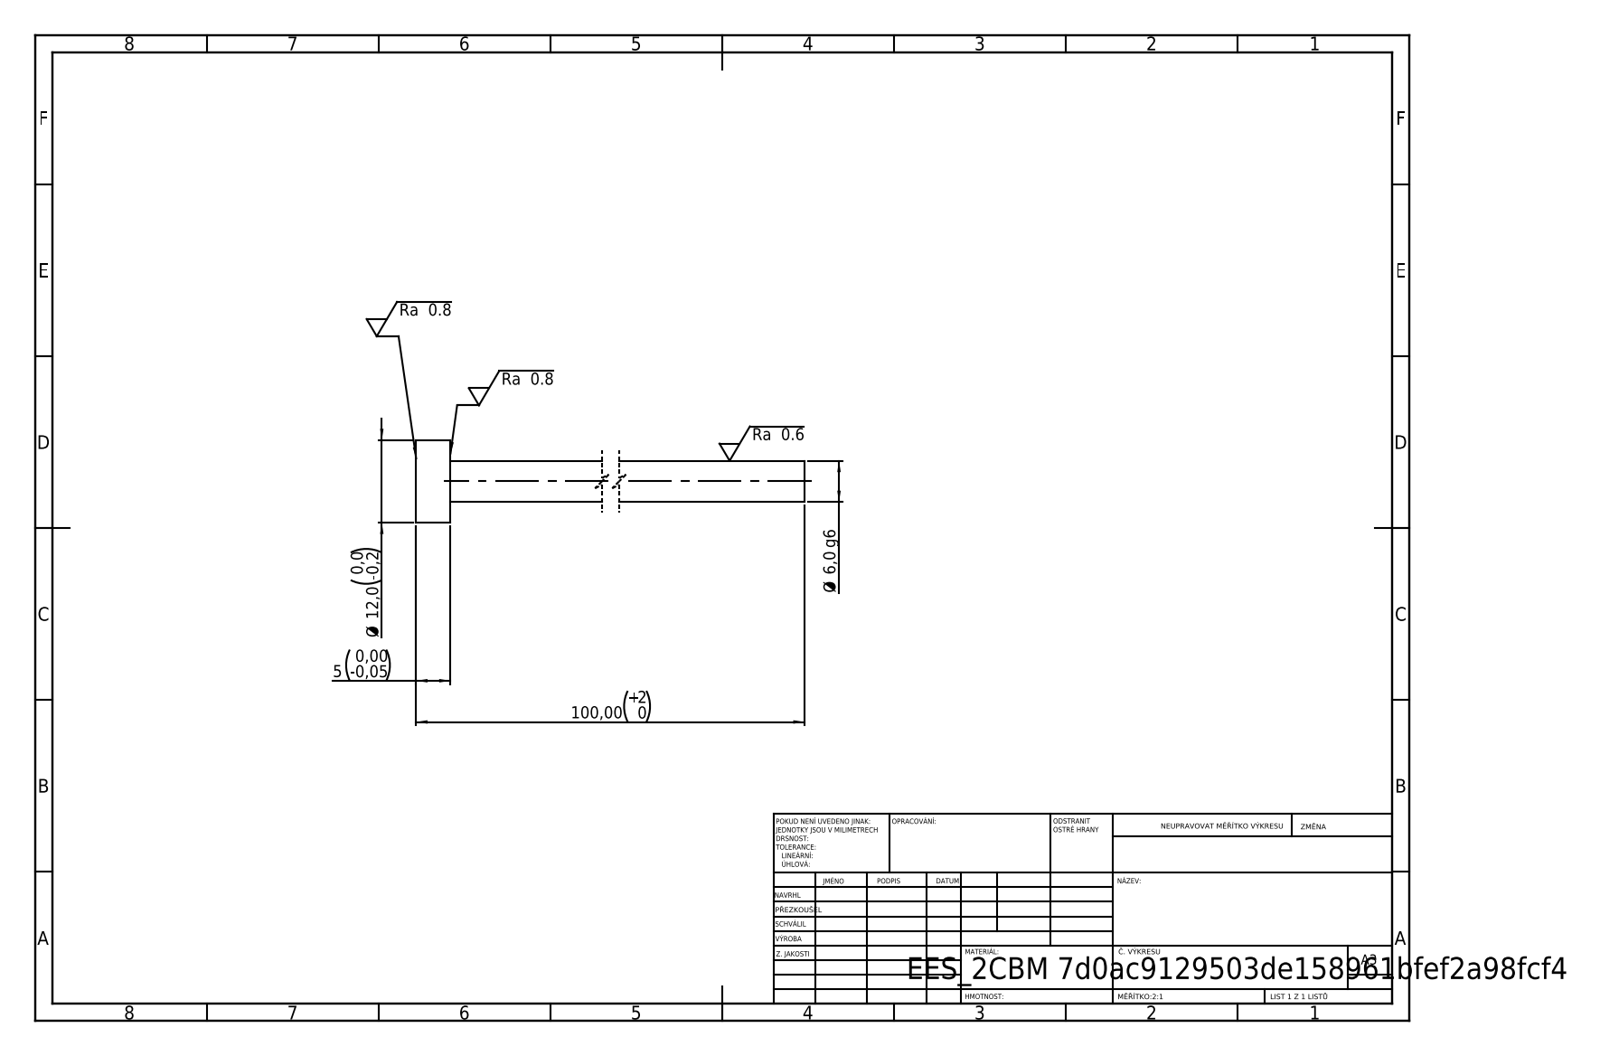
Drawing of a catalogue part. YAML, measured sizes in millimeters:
step_written_by: "SolidWorks 2019 (CONFIG_CONTROL_DESIGN)"
units: millimeters
bodies: {solids: 1, faces: 7, planar: 3, cylindrical: 4, other: 0}
overall_size: [100, 12, 12]
volume: 3252
surface_area: 2205
round_bosses_or_shafts:
  - {diameter: 12, count: 1}
  - {diameter: 6, count: 1}
face_to_face_distances: [5, 100, 95]
